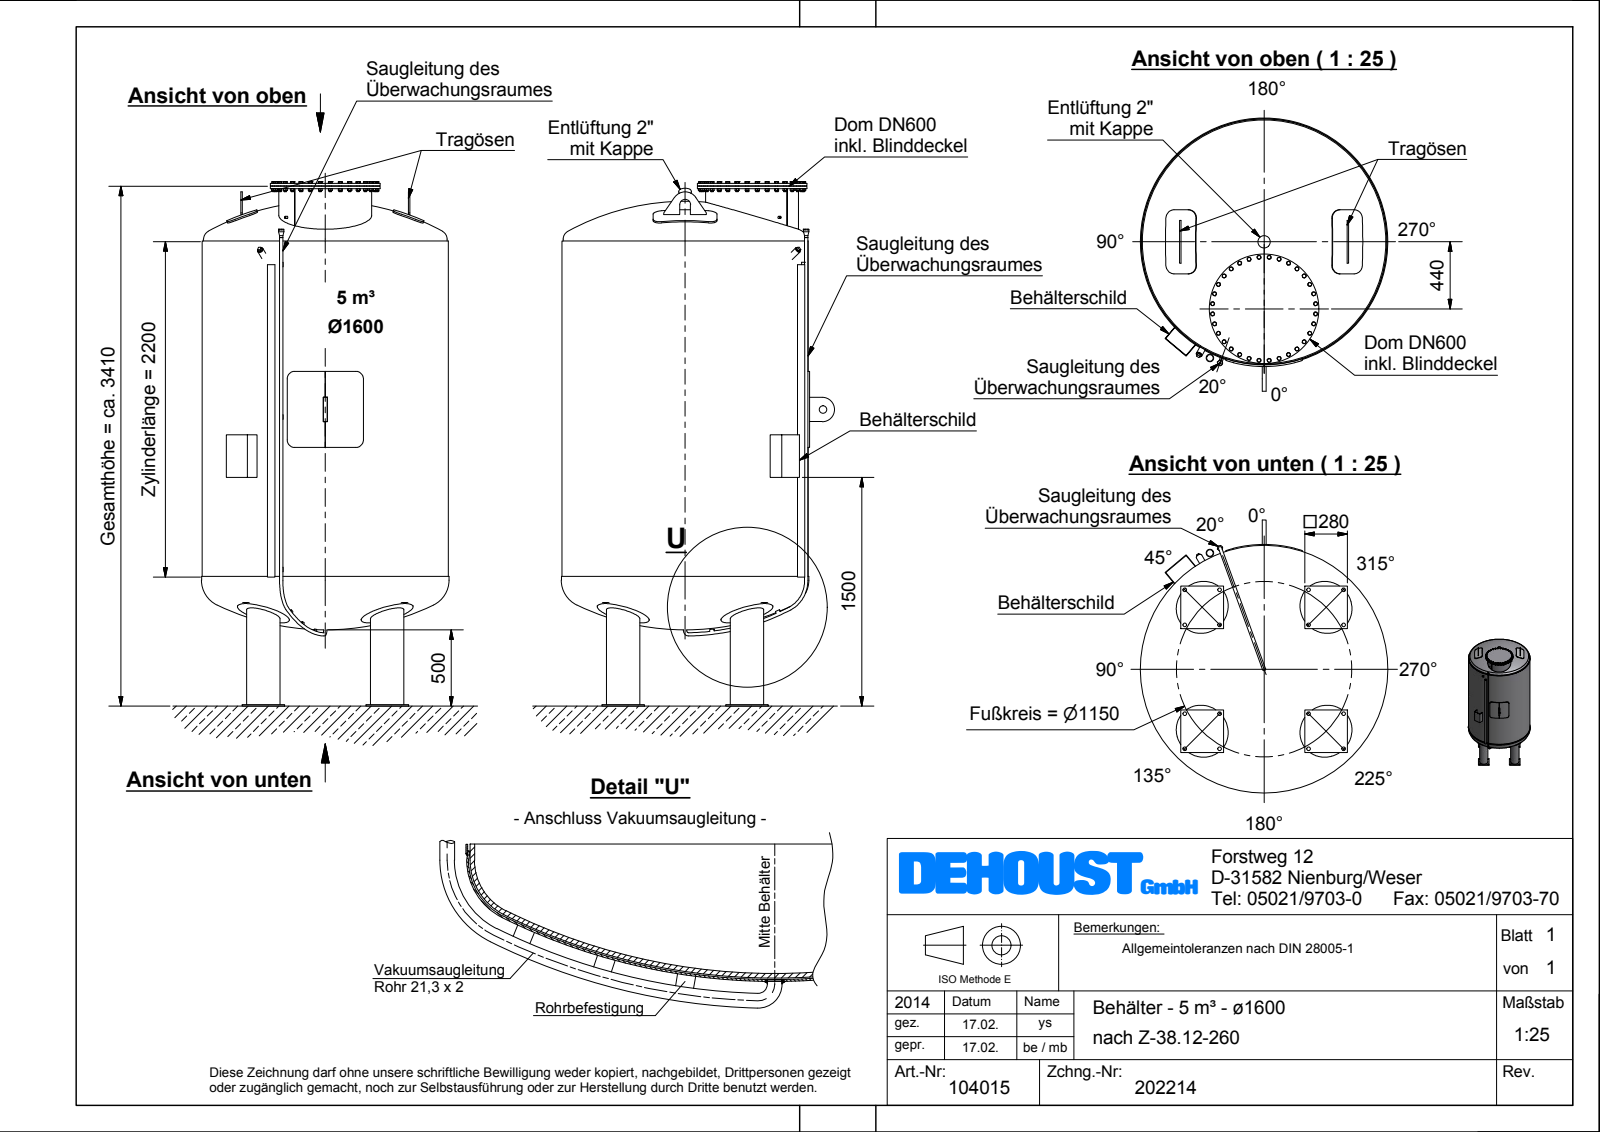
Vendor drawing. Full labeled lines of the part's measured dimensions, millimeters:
Part name (STEP PRODUCT): Z-38_12-260_Beh\S\dlter_\S\x1600_005m\S\3_Dichte=1,0
STEP written by: Autodesk Inventor 2012 (AUTOMOTIVE_DESIGN)
Units: millimetres
Bodies: 7 solids, 1149 faces (675 planar, 150 cylindrical, 324 other)
Overall size (bounding box): 3439.34 × 1720.38 × 1624
Volume: 5 061 000 000 mm³ · Surface area: 27 100 000 mm²
Round holes (diameter × count): ⌀209.1 ×4, ⌀598 ×1, ⌀1590 ×1
Round bosses / shafts (diameter × count): ⌀22.5 ×32, ⌀16 ×32, ⌀350 ×4, ⌀219.1 ×4, ⌀21.3 ×2, ⌀1624 ×1, ⌀1616 ×1, ⌀1600 ×1
Partial cylindrical surfaces — rounded edges, fillets, slot ends (radius × count): R56 ×8, R50 ×4, R35 ×2, R85 ×2, R80 ×1, R818 ×1
Main face-to-face distances: 379.09, 344.09, 35, 3429.34, 10, 3050.25, 3394.34, 3040.25, 3384.34, 3419.34
Hole centre spacings: 575, 813.17, 407.96, 939.16, 1150, 440
